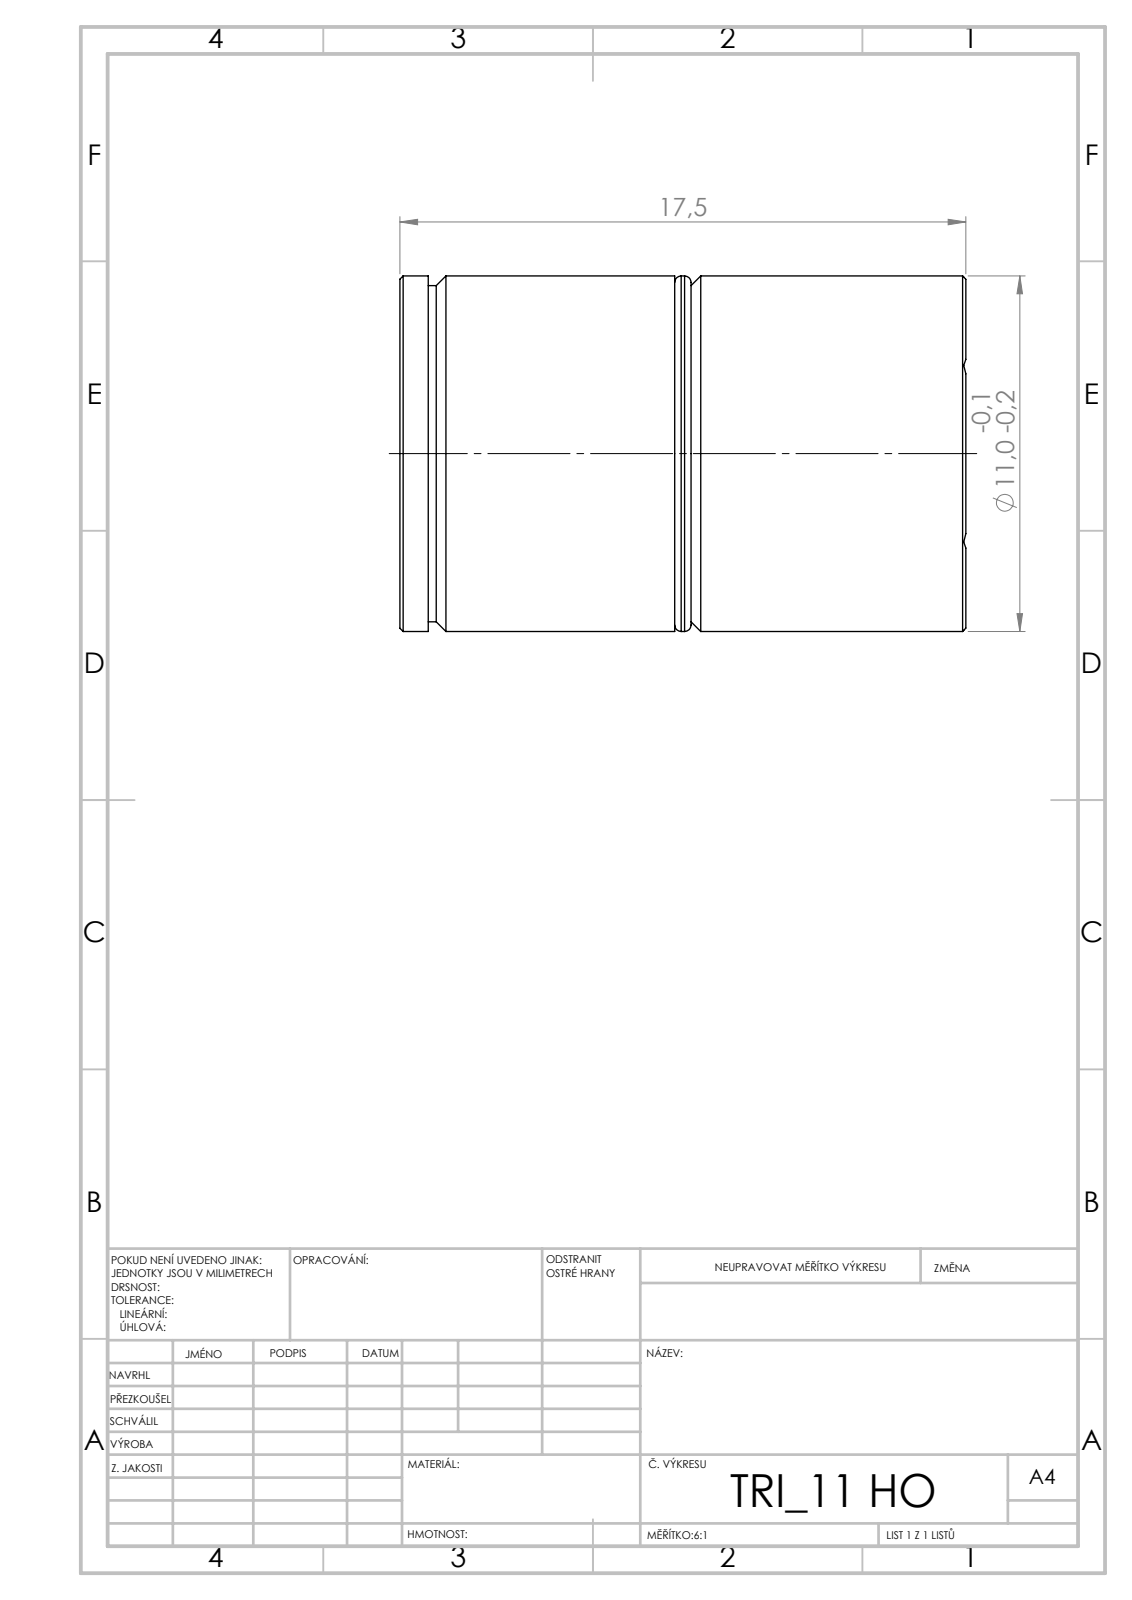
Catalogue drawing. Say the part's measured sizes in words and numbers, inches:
Its 3-D file was written by "SolidWorks 2019 (CONFIG_CONTROL_DESIGN)". It is 2 solids with 48 faces: 24 planar, 12 cylindrical and 12 other. Overall it measures 0.689 by 0.433 by 0.433 inches. Its volume is 0.099 cubic inches and its surface area 1.623 square inches. Round bosses or shafts: 1 of diameter 0.433, 1 of diameter 0.409. The main face-to-face distances are 0.335, 0.354, 0.02, 0.295, 0.315, 0.65, 0.362, 0.039, 0.689, 0.655.
